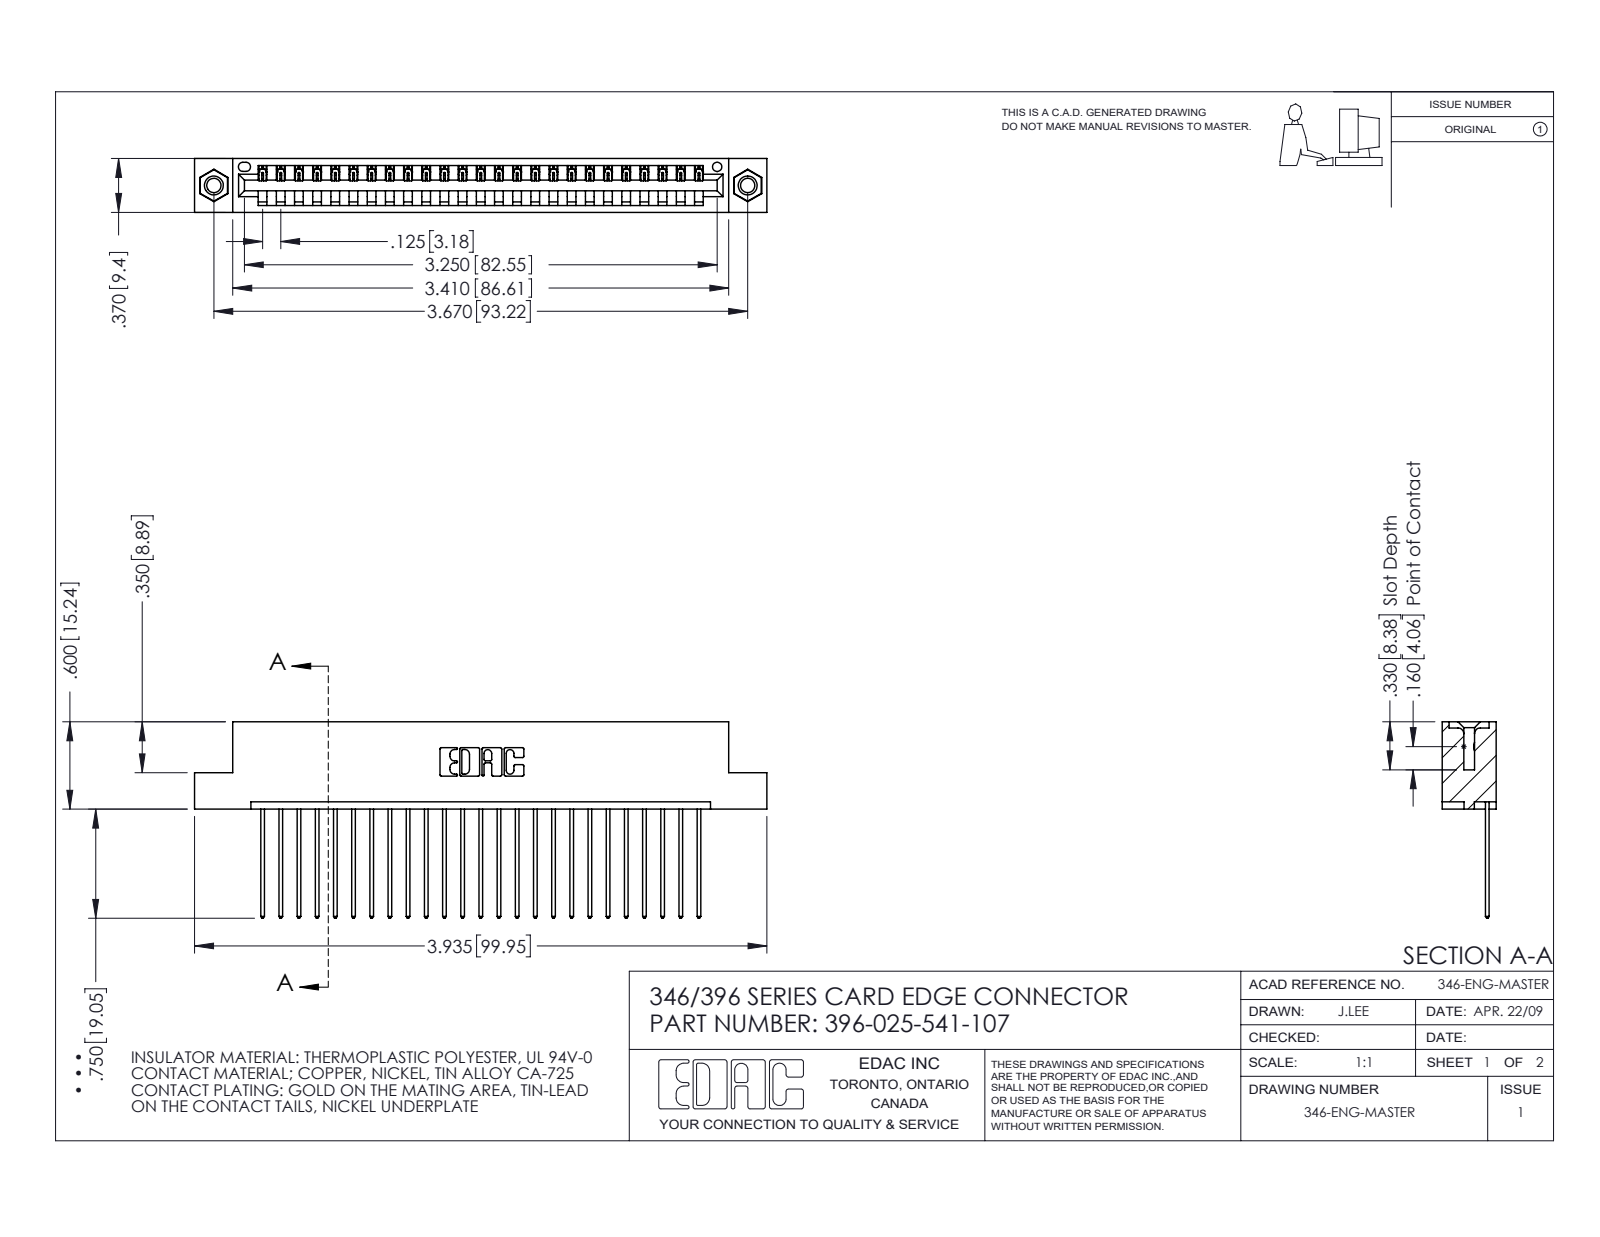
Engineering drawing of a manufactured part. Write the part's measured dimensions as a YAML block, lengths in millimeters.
part_name: "346 Part_Flush Mounting Lugs - 0.156 Dia-TI; 345-250-001_345-250-005-103; 396-025-541-107; 345-292-001_345-293-141"
step_written_by: "SolidWorks 2016 (CONFIG_CONTROL_DESIGN)"
units: millimeters
bodies: {solids: 28, faces: 1632, planar: 1108, cylindrical: 508, other: 16}
overall_size: [99.9, 34.3, 9.4]
volume: 9520
surface_area: 12240
round_holes:
  - {diameter: 2.5, count: 2}
  - {diameter: 3.2, count: 2}
  - {diameter: 4, count: 2}
  - {diameter: 1.6, count: 1}
round_bosses_or_shafts:
  - {diameter: 3.9, count: 2}
partial_cylinders:
  - {radius: 0.2, count: 50}
  - {radius: 0.3, count: 50}
  - {radius: 0.3, count: 22}
  - {radius: 0.2, count: 6}
  - {radius: 0.8, count: 6}
  - {radius: 0.7, count: 3}
  - {radius: 0.8, count: 2}
  - {radius: 1, count: 2}
face_to_face_distances: [1.2, 8.2, 9.4, 6.4, 1.8, 7.6, 0.6, 3.8, 5.6, 2.5]
hole_center_spacings: [6.2, 87.9, 93.2]
